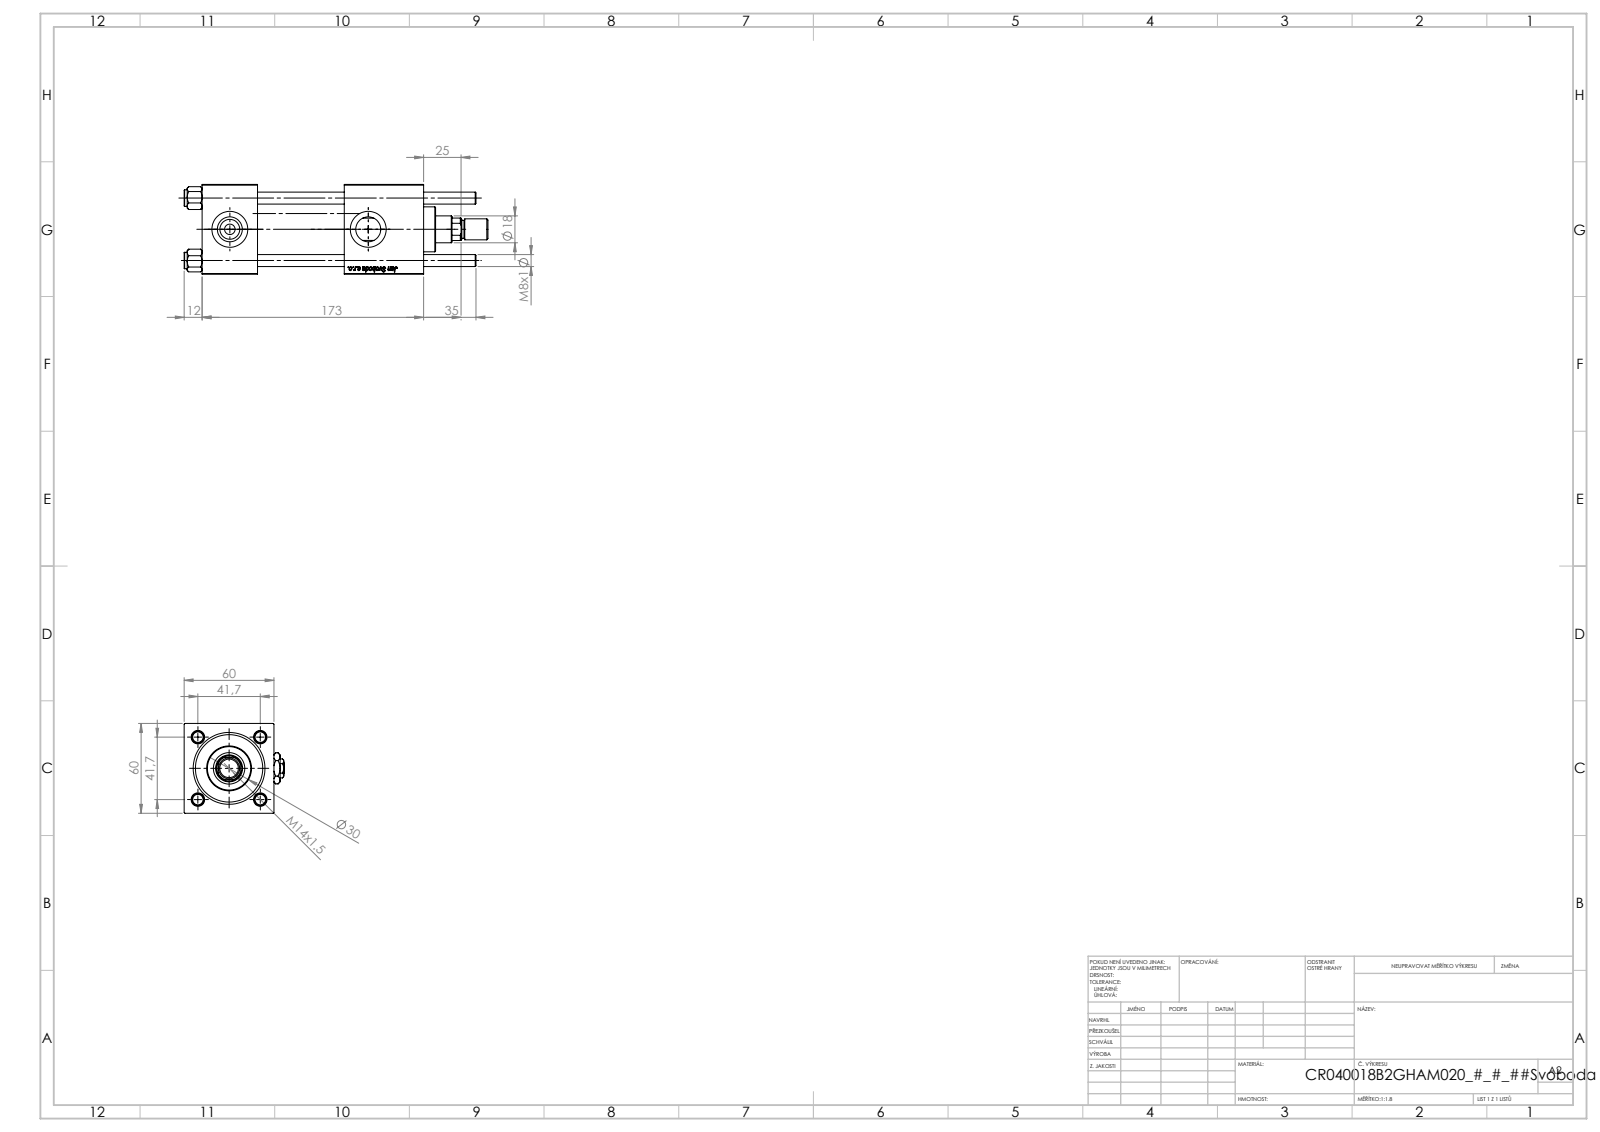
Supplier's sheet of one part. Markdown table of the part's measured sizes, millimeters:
| quantity | value |
| --- | --- |
| part name | V215CR_B_TYCINKA; V215_VC_A; Zatka_pro_OIL_PORT; V215CR_B-1 (+3 more) |
| STEP written by | SolidWorks 2019 (CONFIG_CONTROL_DESIGN) |
| units | millimeters |
| bodies | 13 solids, 1225 faces (461 planar, 88 cylindrical, 676 other) |
| overall size | 203 × 67 × 60 |
| volume | 415 276 mm³ |
| surface area | 116 532 mm² |
| round holes (diameter × count) | 8 × 4, 7 × 2, 16.66 × 2, 24 × 2, 8.5 × 1, 18 × 1, 21 × 1, 31 × 1, 40 × 1, 45 × 1 |
| round bosses / shafts (diameter × count) | 11 × 4, 46 × 1, 30 × 1, 14 × 1, 12 × 1 |
| partial cylindrical surfaces (radius × count) | 8.5 × 1 |
| main face-to-face distances | 60, 37, 148, 111, 58, 53, 95, 119.3, 82.3, 24.3 |
| hole center spacings | 29.49, 41.7, 58.97, 92.5 |
